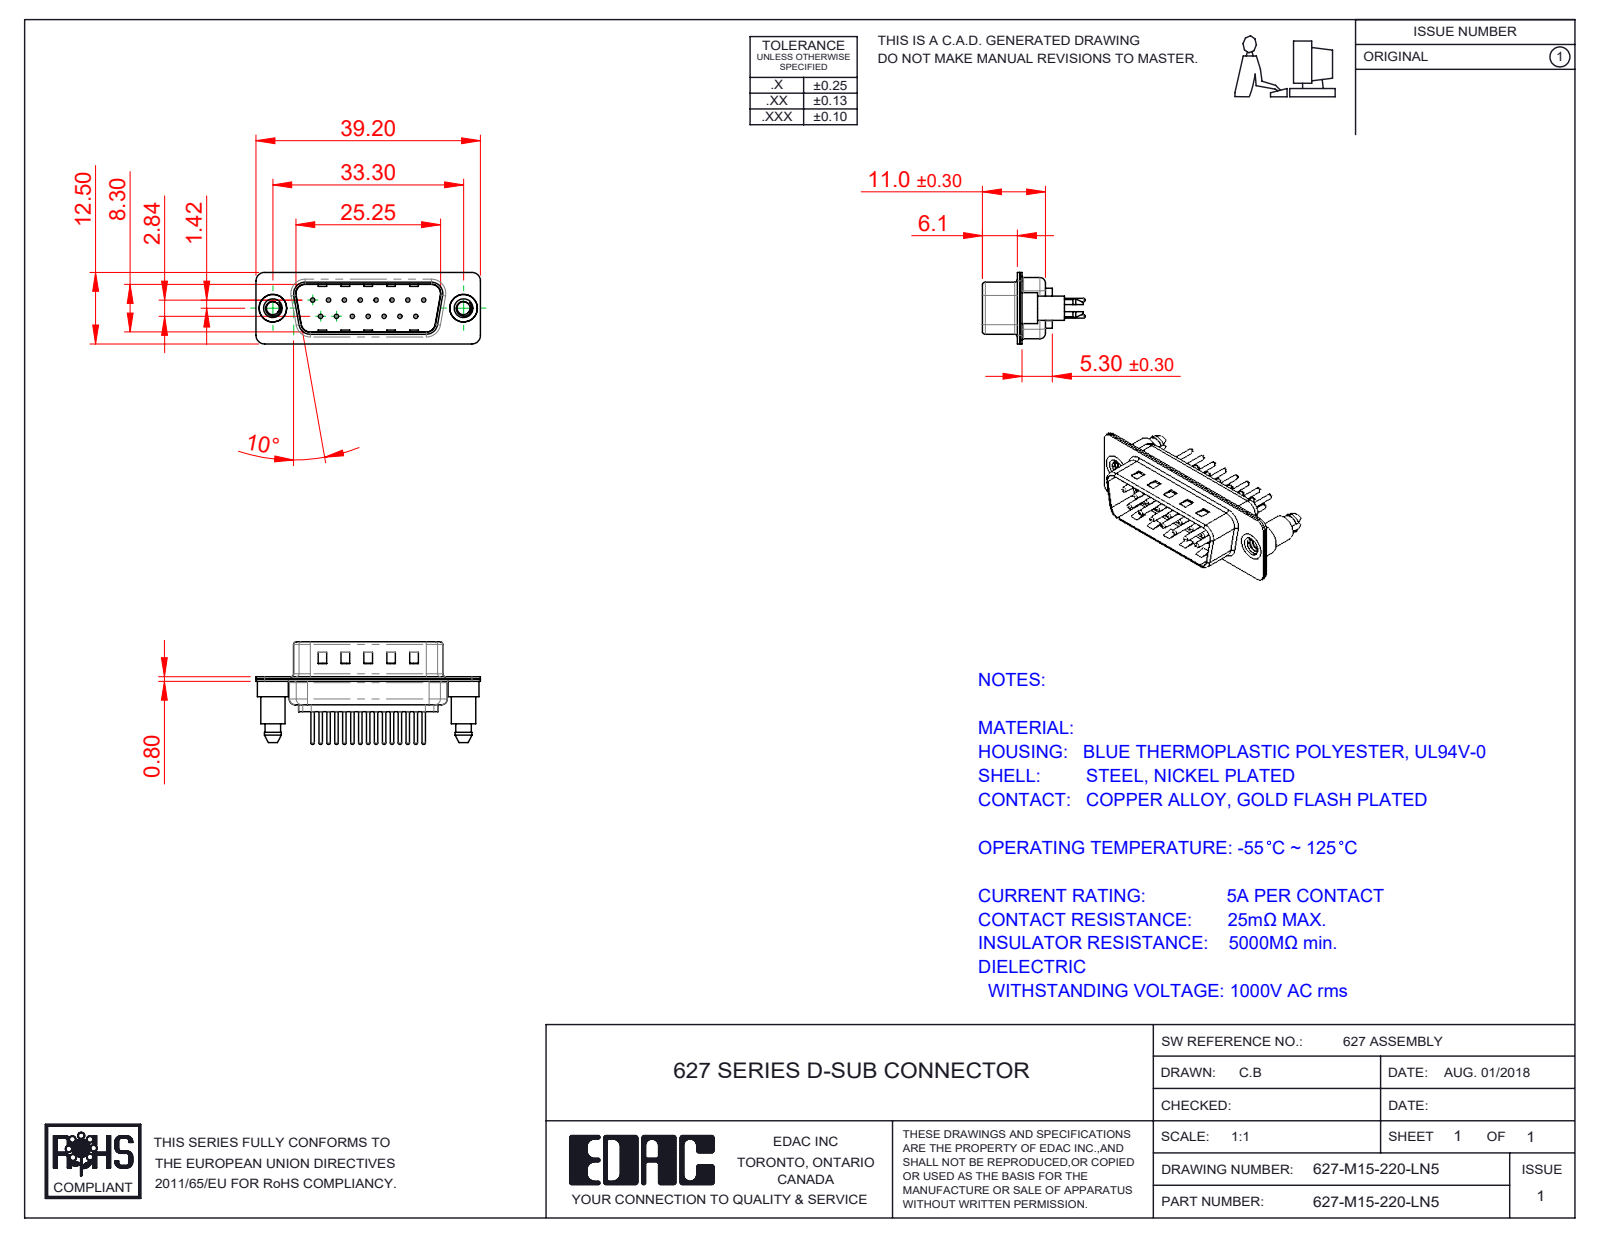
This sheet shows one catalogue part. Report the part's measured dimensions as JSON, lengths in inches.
{"part_name": "627M 4-40 Threaded Boardlock; 627M Housing_15 Contacts; 627-M15-220-LN5; 627M Contact Row 1_20 (+3 more)", "step_written_by": "SolidWorks 2020 (CONFIG_CONTROL_DESIGN)", "units": "inches", "bodies": {"solids": 20, "faces": 945, "planar": 260, "cylindrical": 375, "other": 310}, "overall_size": [1.543, 0.705, 0.492], "volume_in3": 0.121, "surface_area_in2": 7.969, "round_holes": [[0.03, 15], [0.063, 15], [0.079, 15], [0.089, 2], [0.157, 2], [0.189, 2]], "round_bosses_or_shafts": [[0.059, 15], [0.024, 15], [0.213, 2], [0.193, 2], [0.167, 2]], "partial_cylinders_radius": [[0.059, 18], [0.079, 12], [0.063, 10], [0.02, 8], [0.01, 4], [0.024, 4], [0.026, 4], [0.035, 4]], "face_to_face_distances": [0.016, 0.031, 0.374, 0.358, 0.343, 0.39, 0.209, 0.047, 0.24, 0.224], "hole_center_spacings": [0.124, 0.109, 0.218, 0.327, 0.436, 0.198, 0.198, 0.294]}
